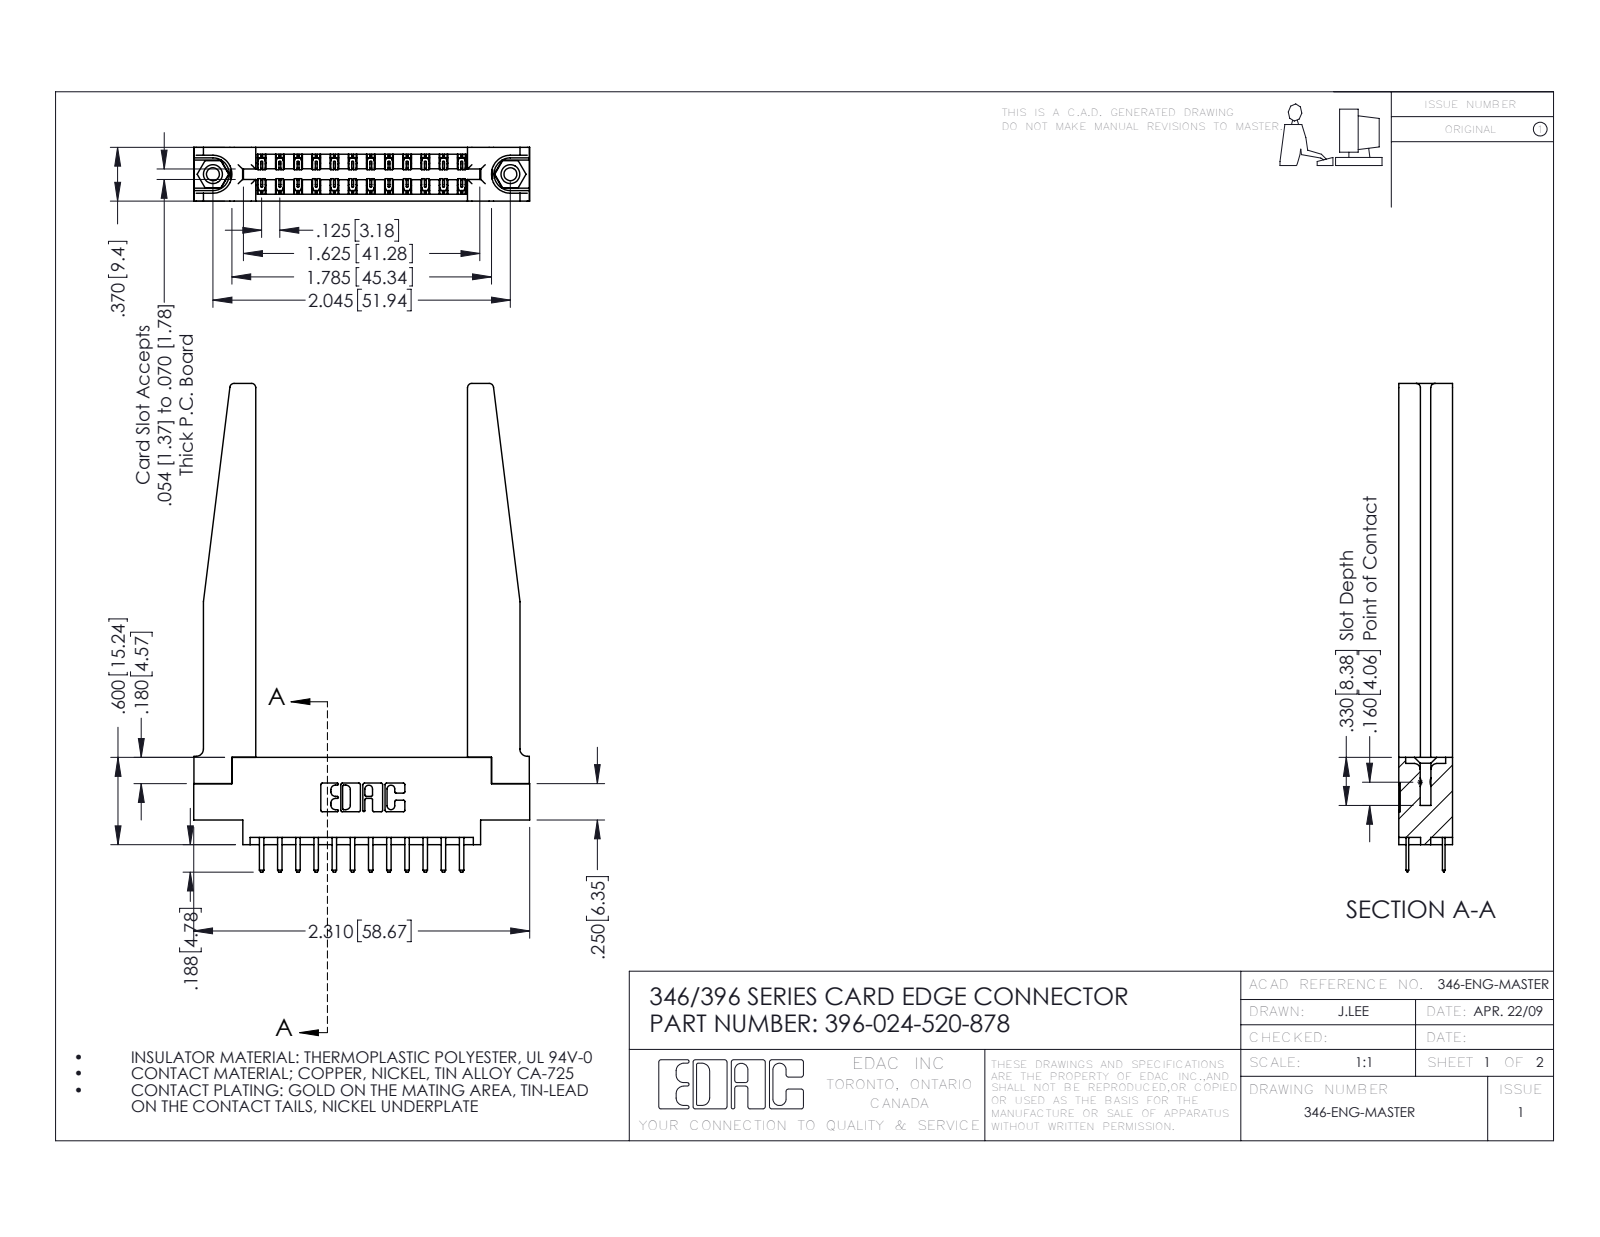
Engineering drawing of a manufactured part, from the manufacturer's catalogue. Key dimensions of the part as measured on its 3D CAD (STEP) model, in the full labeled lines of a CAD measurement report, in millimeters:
Part name (STEP PRODUCT): 345-292-001_345-293-120; 346-220-078_345-220-078; 396-024-520-878; 345-250-001_345-250-001-102 (+1 more)
STEP written by: SolidWorks 2016 (CONFIG_CONTROL_DESIGN)
Units: millimetres
Bodies: 29 solids, 1704 faces (1110 planar, 542 cylindrical, 52 other)
Overall size (bounding box): 85.3 × 58.7 × 9.4
Volume: 12 200 mm³ · Surface area: 13 540 mm²
Round holes (diameter × count): ⌀2.3 ×2, ⌀3.2 ×2, ⌀4 ×2, ⌀1.6 ×1
Round bosses / shafts (diameter × count): ⌀3.9 ×2
Partial cylindrical surfaces — rounded edges, fillets, slot ends (radius × count): R0.2 ×36, R0.3 ×28, R0.3 ×22, R0.8 ×8, R0.2 ×6, R0.8 ×6, R0.7 ×3, R0.4 ×2
Main face-to-face distances: 9.4, 3.8, 1.8, 3.8, 1.2, 8.2, 6.4, 2.6, 5.6, 4.4
Hole centre spacings: 6.2, 46.7, 51.9
